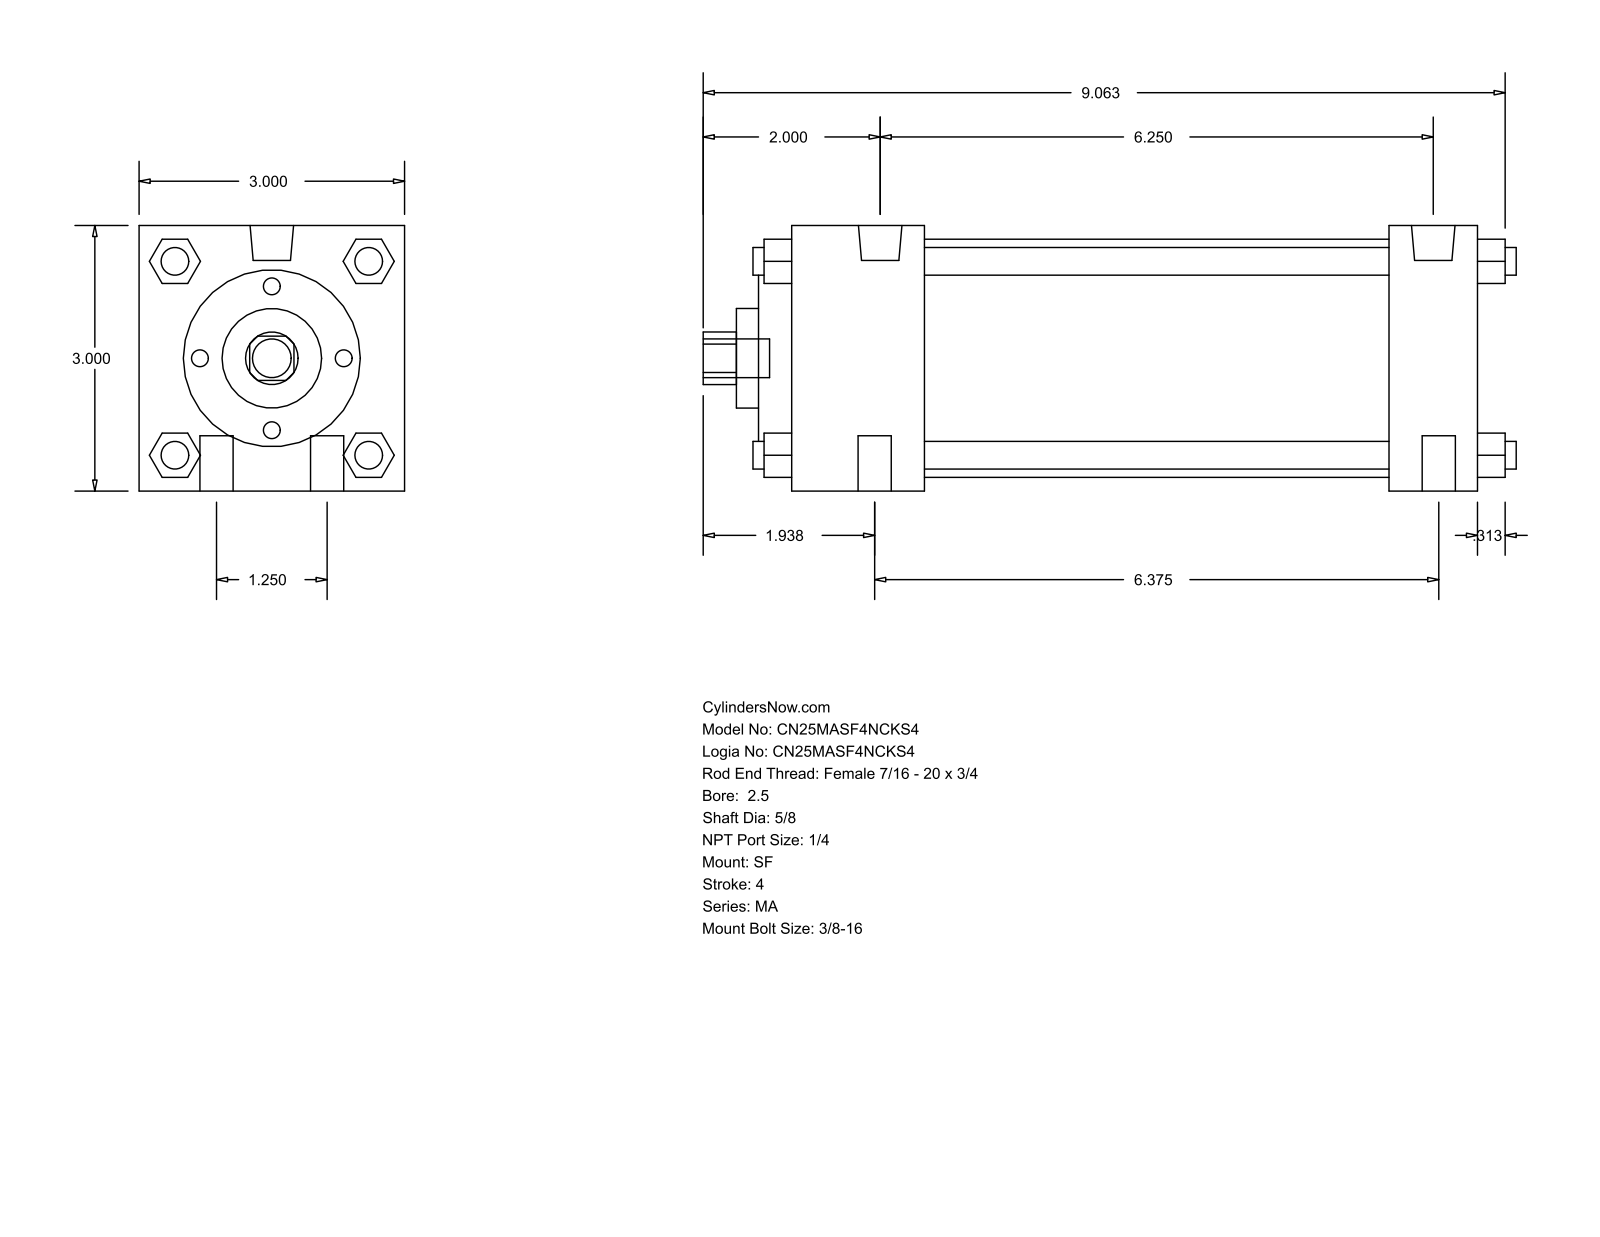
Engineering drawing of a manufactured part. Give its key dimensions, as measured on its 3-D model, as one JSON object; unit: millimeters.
{"part_name": "MA_SF__0250_0.625", "step_written_by": "GSSL Pune (CONFIG_CONTROL_DESIGN)", "units": "millimeters", "bodies": {"solids": 0, "faces": 126, "planar": 95, "cylindrical": 31, "other": 0}, "overall_size": [233.36, 76.2, 76.2], "round_holes": [[15.88, 1], [28.57, 1], [50.8, 1], [68.33, 1]], "round_bosses_or_shafts": [[7.94, 6], [9.53, 4], [12.49, 2], [11.11, 1]], "partial_cylinders_radius": [[7.54, 1]], "face_to_face_distances": [76.2, 196.85, 25.4, 171.45, 38.1, 133.35, 158.75, 12.7, 9.52, 47.62]}
